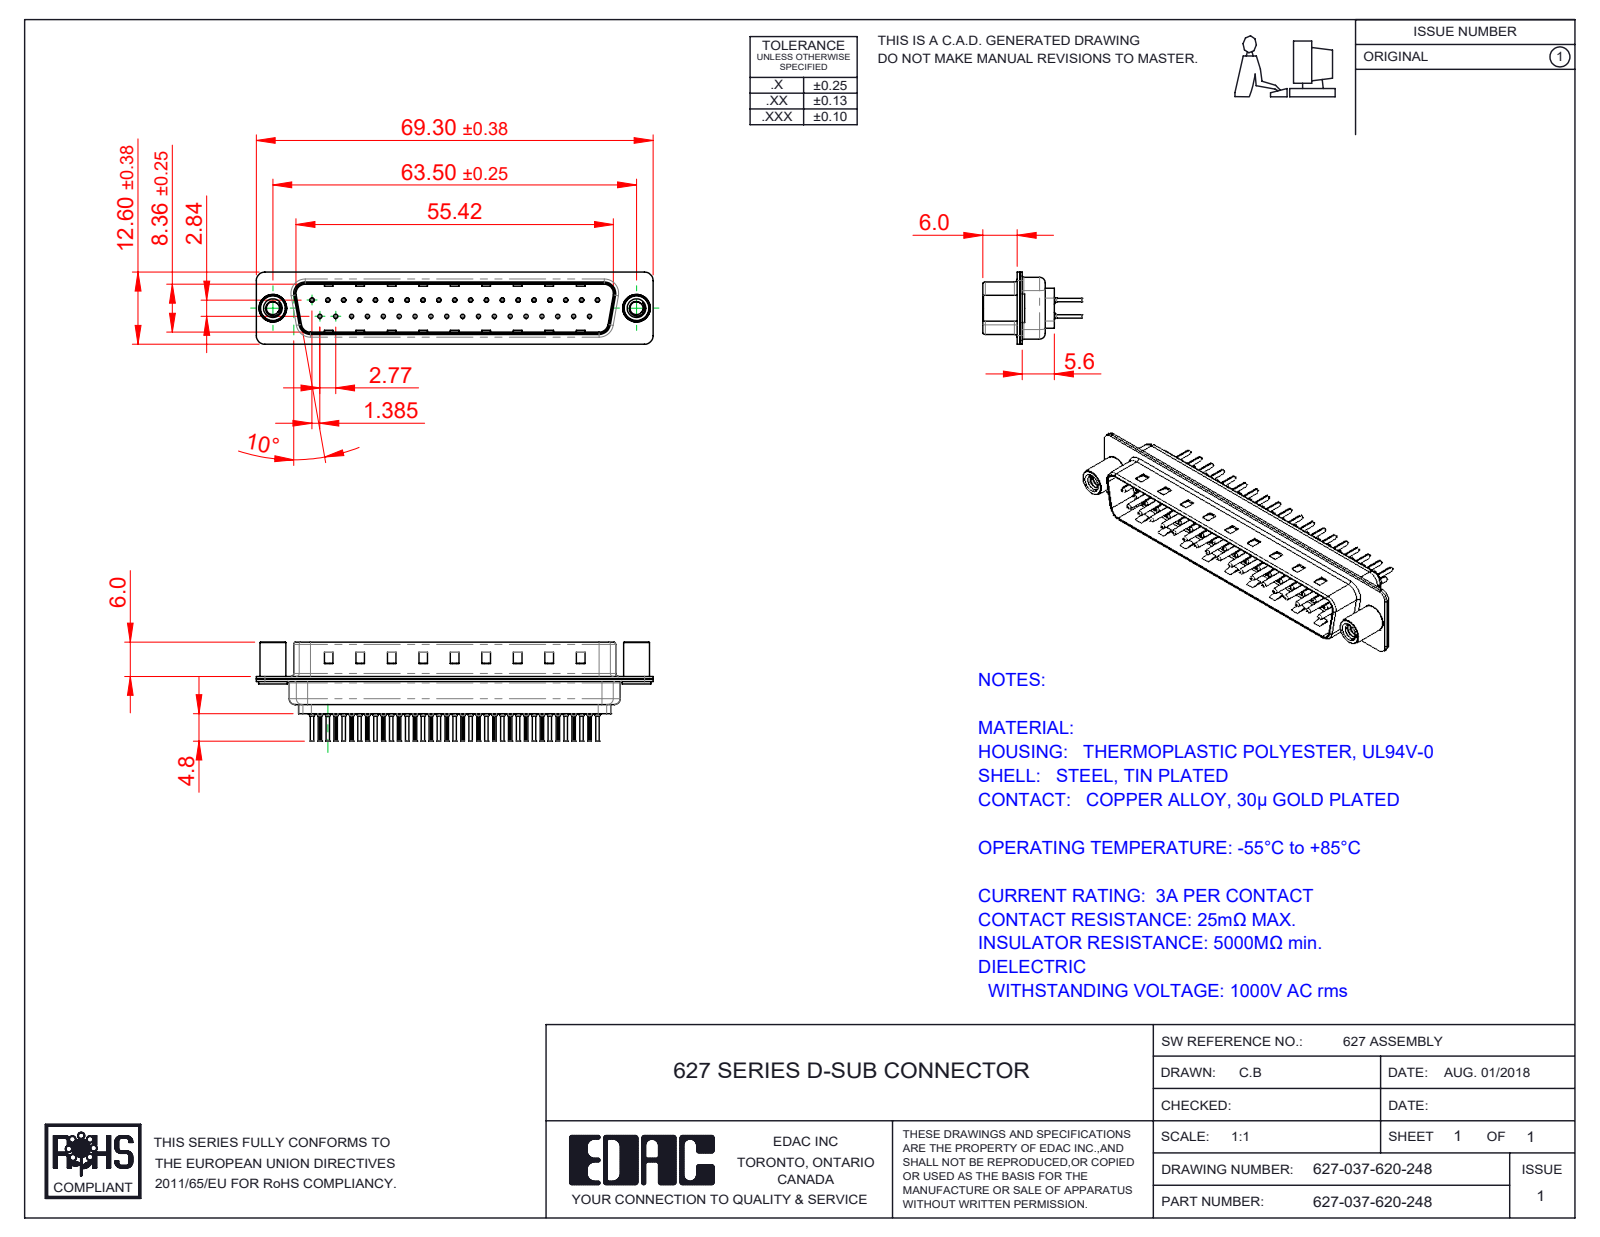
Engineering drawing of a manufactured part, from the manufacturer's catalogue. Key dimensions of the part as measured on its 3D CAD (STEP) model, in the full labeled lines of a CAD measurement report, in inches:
Part name (STEP PRODUCT): 627 Housing_37 LP; 627 4-40 Threaded Standoff; 627 Shell Front_37 Contacts; 627 Contact Row 2_20L (+3 more)
STEP written by: SolidWorks 2020 (CONFIG_CONTROL_DESIGN)
Units: inches
Bodies: 42 solids, 4072 faces (1093 planar, 1538 cylindrical, 1441 other)
Overall size (bounding box): 2.728 × 0.681 × 0.496
Volume: 0.23 in³ · Surface area: 16.86 in²
Round holes (diameter × count): ⌀0.008 ×37, ⌀0.014 ×37, ⌀0.043 ×37, ⌀0.063 ×37, ⌀0.089 ×2, ⌀0.157 ×2, ⌀0.189 ×2
Round bosses / shafts (diameter × count): ⌀0.079 ×37, ⌀0.059 ×37, ⌀0.03 ×37, ⌀0.024 ×37, ⌀0.197 ×2, ⌀0.193 ×2, ⌀0.177 ×2
Partial cylindrical surfaces — rounded edges, fillets, slot ends (radius × count): R0.004 ×74, R0.059 ×16, R0.079 ×12, R0.02 ×8, R0.063 ×8, R0.01 ×4, R0.024 ×4, R0.026 ×4
Main face-to-face distances: 0.016, 0.032, 0.377, 0.018, 0.345, 0.059, 0.035, 0.055, 0.238, 0.017
Hole centre spacings: 0.124, 0.109, 0.218, 0.327, 0.198, 0.398, 0.436, 0.503
